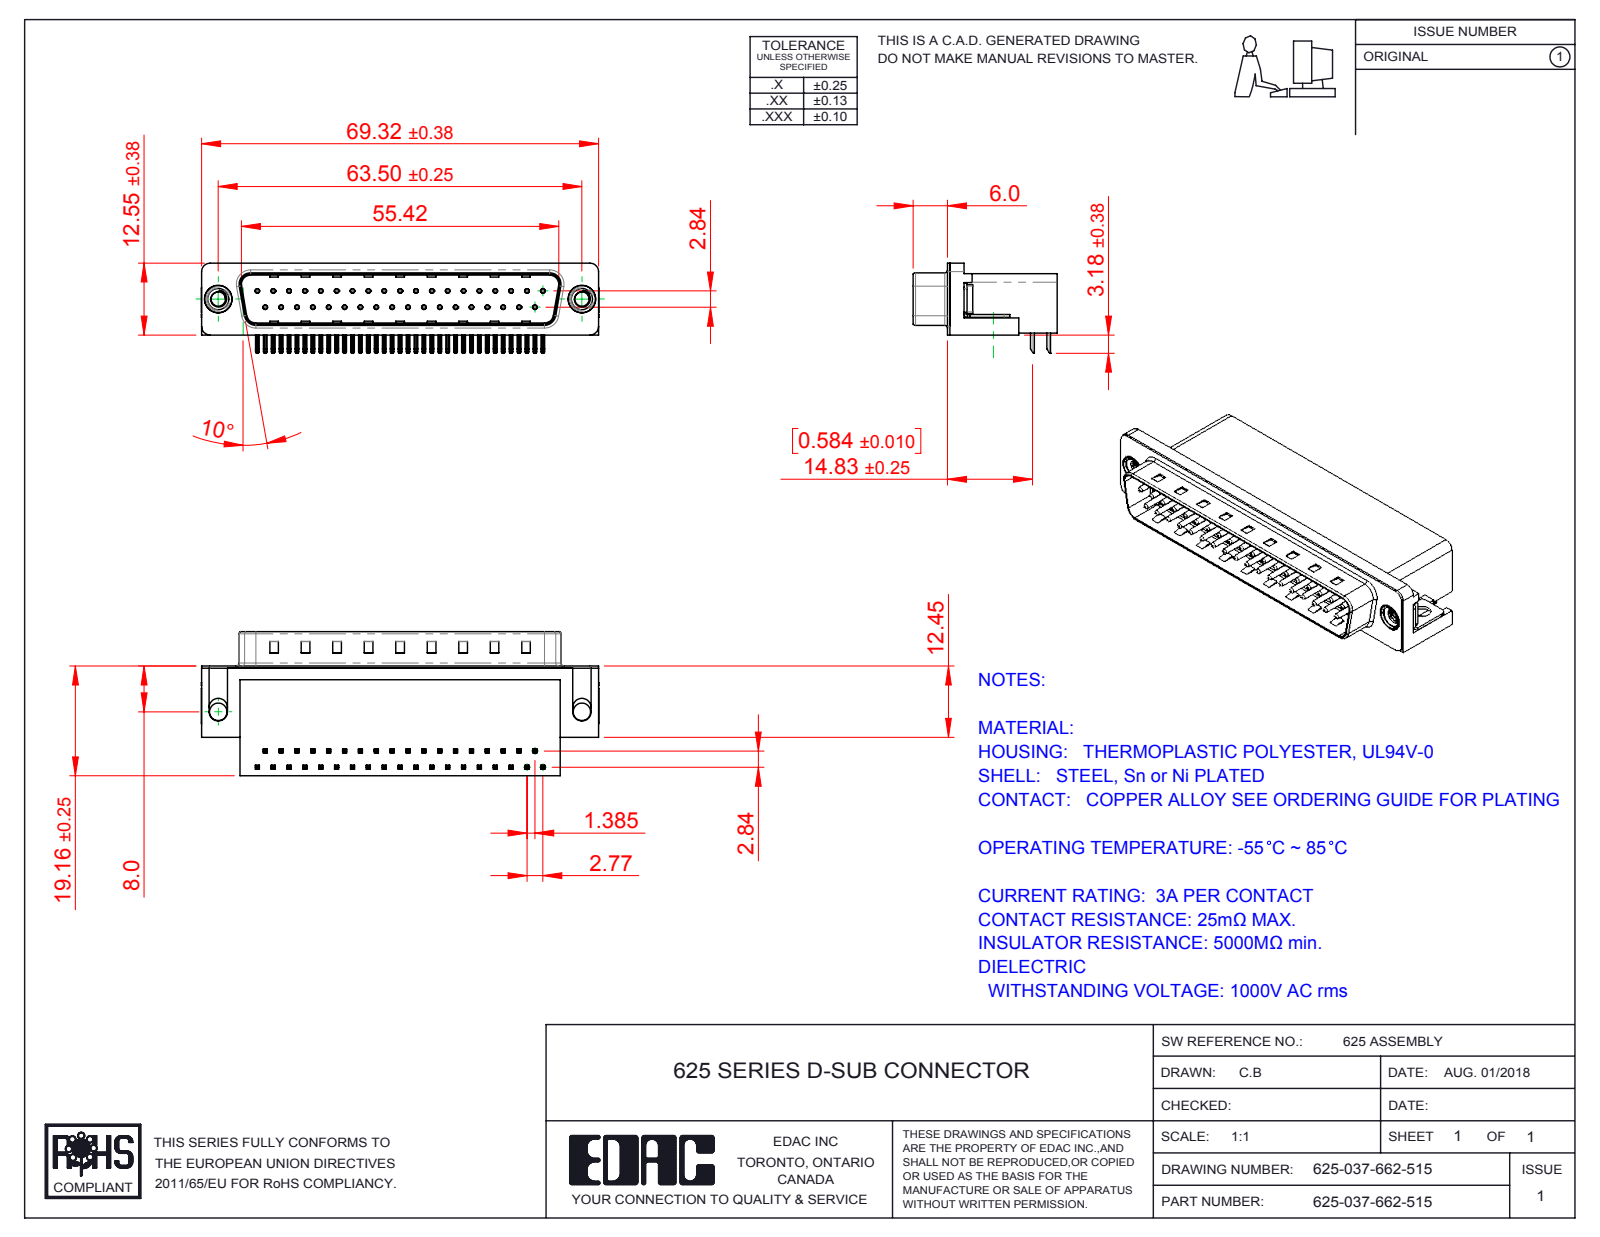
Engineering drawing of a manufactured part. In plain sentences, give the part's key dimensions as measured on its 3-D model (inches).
The part is named "625-037-662-515; 625 Housing_37 Socket; 625 Shell_37 Socket; 625 M3 Threaded Rivet (+3 more)". Its 3-D file was written by "SolidWorks 2016 (CONFIG_CONTROL_DESIGN)". It is 43 solids with 3201 faces: 2013 planar, 921 cylindrical and 267 other. Overall it measures 2.732 by 0.991 by 0.619 inches. Its volume is 0.768 cubic inches and its surface area 18.2 square inches. Round holes: 37 of diameter 0.014, 37 of diameter 0.031, 2 of diameter 0.098, 2 of diameter 0.12, 2 of diameter 0.157, 2 of diameter 0.189, 2 of diameter 0.197. Round bosses or shafts: 37 of diameter 0.03, 2 of diameter 0.193, 2 of diameter 0.187, 2 of diameter 0.154. Partial cylindrical surfaces (rounded edges, fillets, slot ends): 156 of radius 0.01, 74 of radius 0.005, 16 of radius 0.039, 9 of radius 0.02, 8 of radius 0.063, 7 of radius 0.059, 4 of radius 0.035, 4 of radius 0.079. The main face-to-face distances are 0.407, 0.016, 0.739, 0.345, 0.754, 0.112, 0.082, 0.398, 0.069, 0.329. The hole center spacings are 0.124, 0.109, 0.218, 0.327, 0.436, 0.545, 0.763, 0.872.
